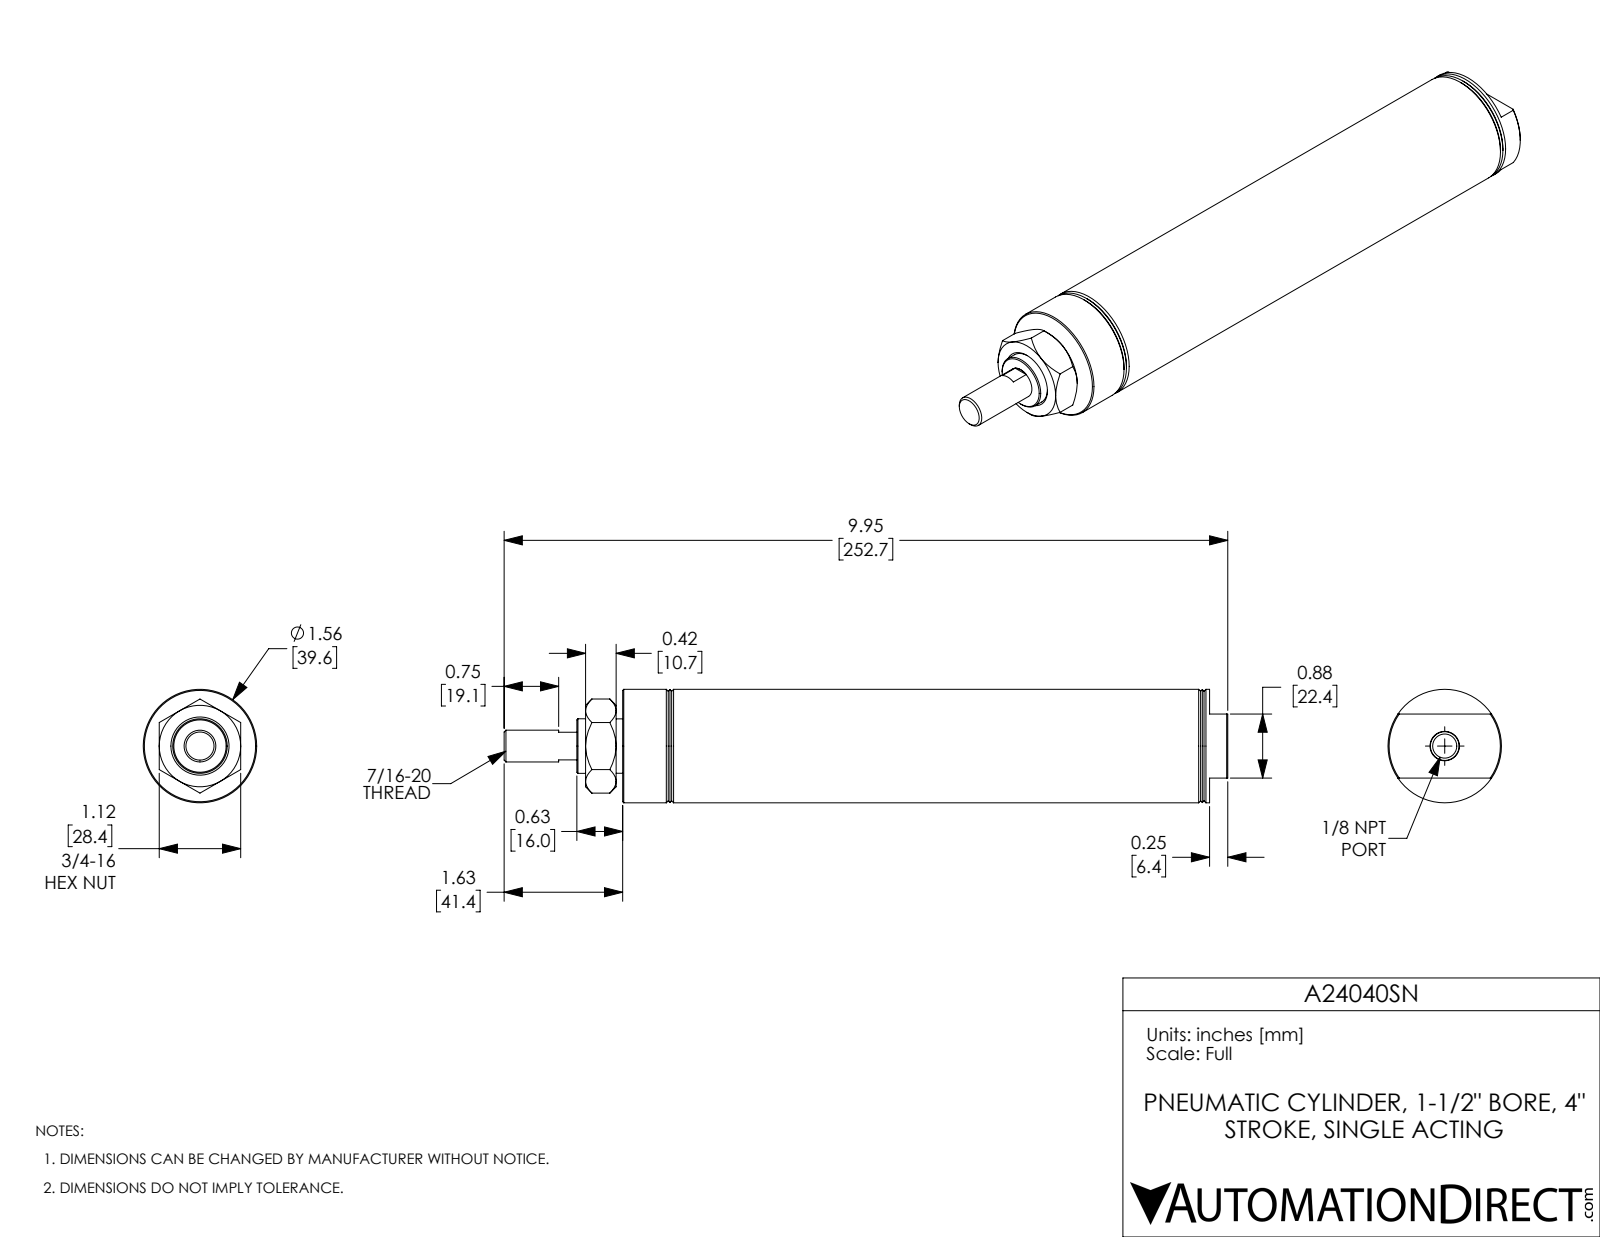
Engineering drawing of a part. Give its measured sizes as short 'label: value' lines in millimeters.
name: A24040SN-MainBody; A24040SN-Rod; A24040SN_Mounting Nut_D-3556; A24040SN
written by: SolidWorks 2017 (AUTOMOTIVE_DESIGN)
unit: mm
bodies: 3 solids, 93 faces (28 planar, 22 cylindrical, 43 other)
size: 252.7 × 39.6 × 39.6
volume: 160 300 mm³; area: 61 920 mm²
holes: 1× ⌀8.4, 1× ⌀11.1, 1× ⌀19.1, 1× ⌀38.1
bosses: 1× ⌀39.6, 1× ⌀19
face distances: 12.7, 114.3, 101.6, 162.8, 150.1, 48.5, 48.5, 61.2, 162.8, 211.3
